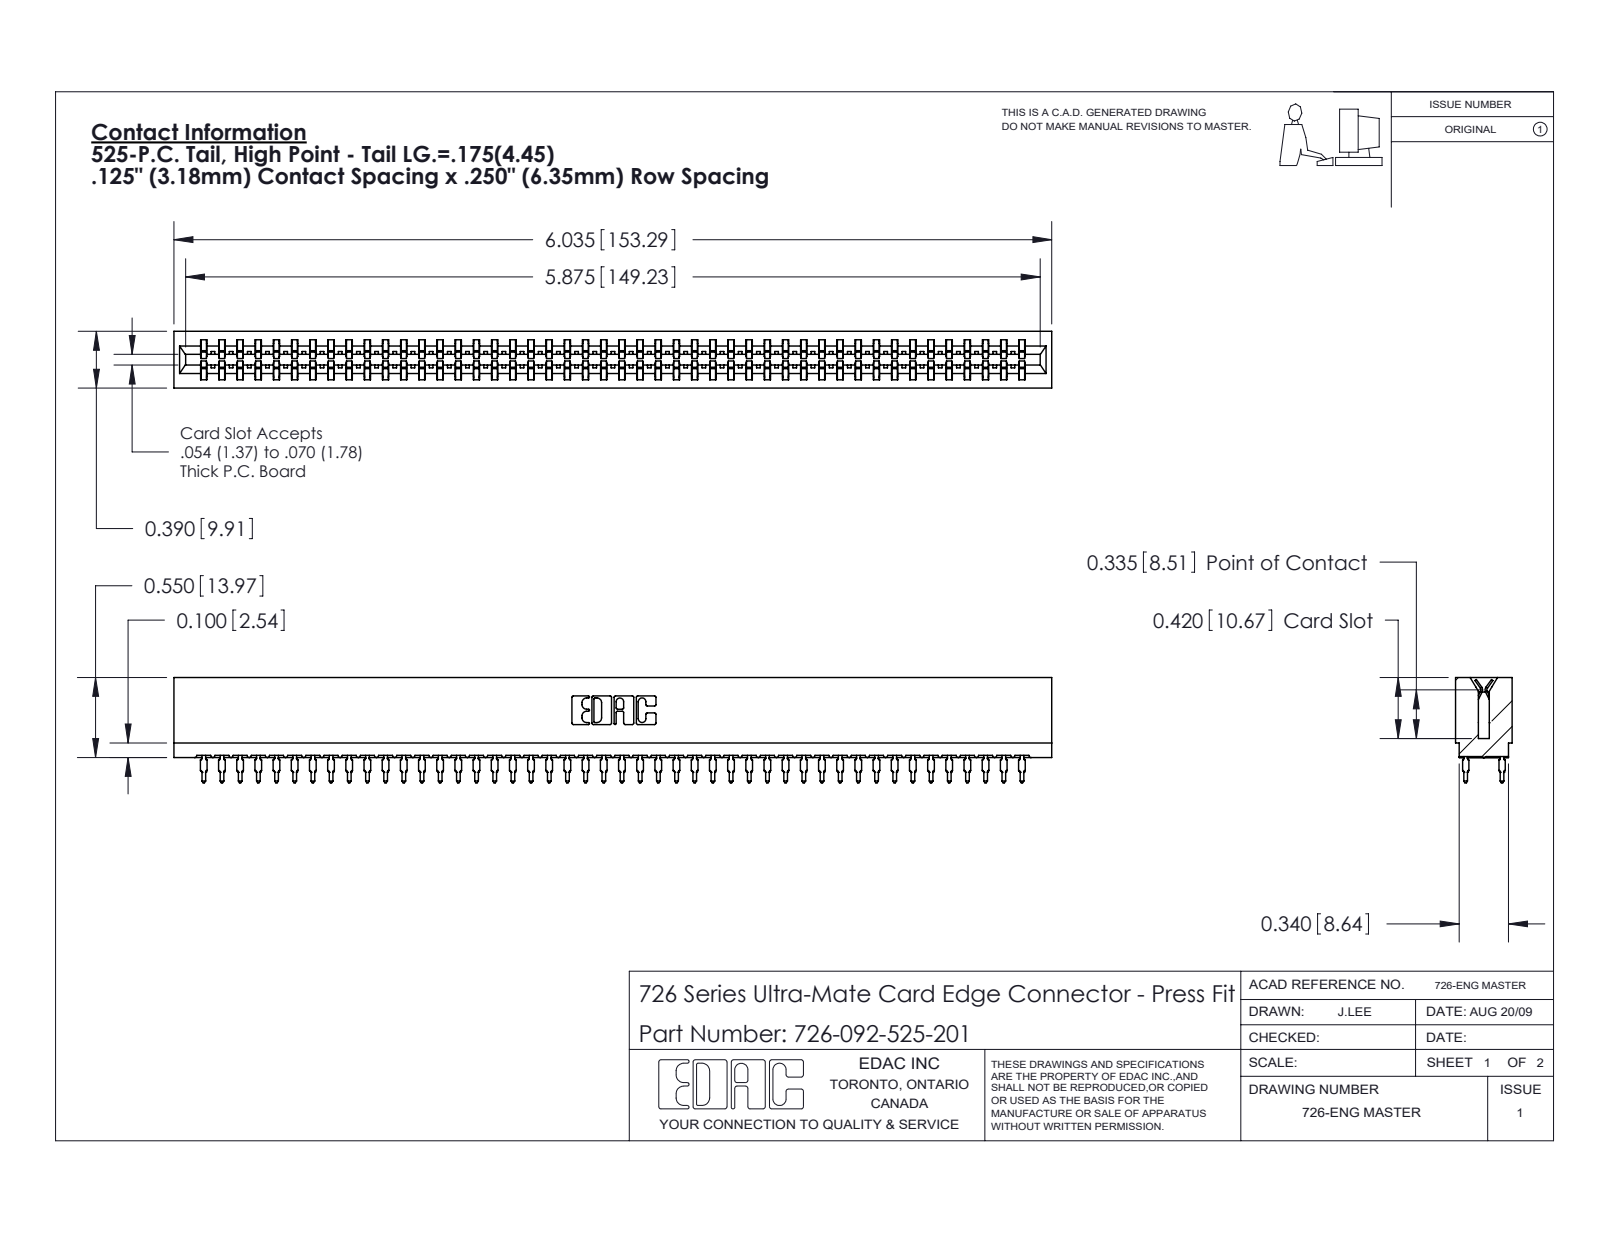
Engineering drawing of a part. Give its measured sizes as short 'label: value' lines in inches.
name: 726 Part_.515 Slot Depth - 01; 746-292-001_525; 726-092-525-201
written by: SolidWorks 2020 (CONFIG_CONTROL_DESIGN)
unit: in
bodies: 93 solids, 8331 faces (4287 planar, 1652 cylindrical, 2392 other)
size: 6.035 × 0.724 × 0.39
volume: 0.857 in³; area: 36.05 in²
rounds: 184× R0.021, 47× R0.015, 22× R0.01, 8× R0.005, 8× R0.011, 6× R0.007, 6× R0.031, 3× R0.026
face distances: 0.057, 0.333, 0.39, 0.025, 0.307, 0.25, 0.275, 0.083, 0.365, 0.032
